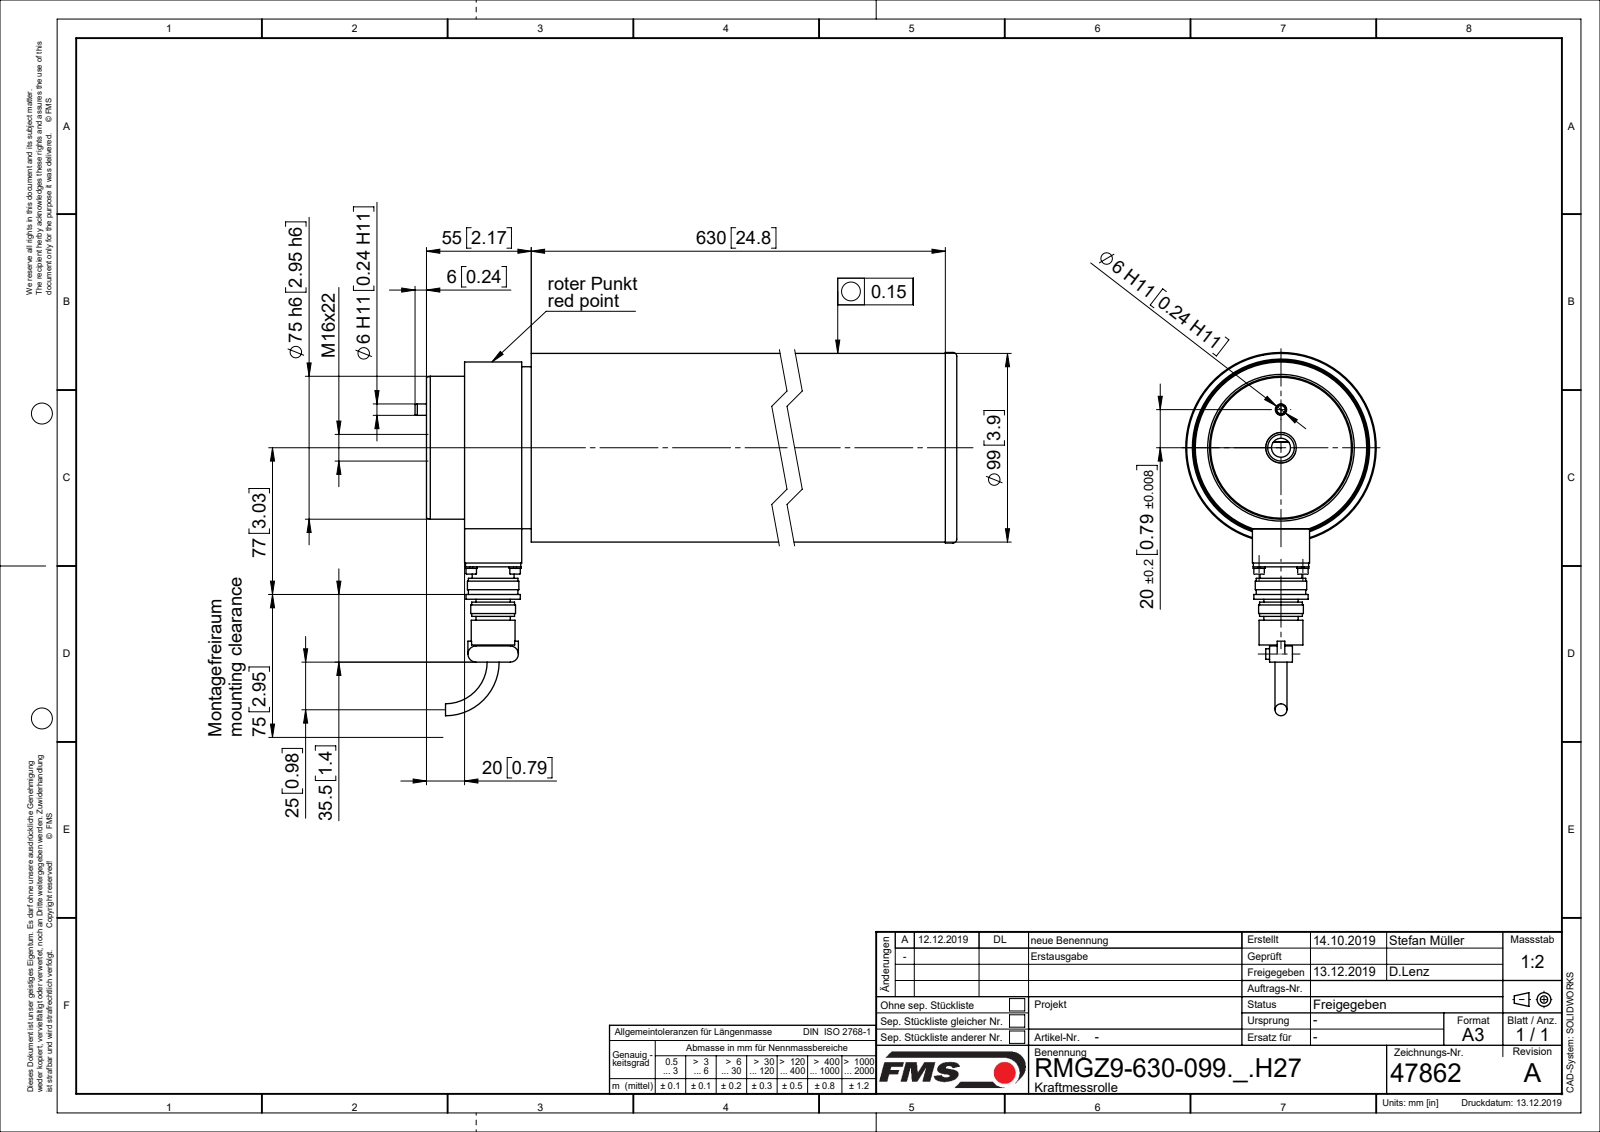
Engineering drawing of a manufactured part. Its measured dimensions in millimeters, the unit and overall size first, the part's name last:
Units: millimetres
Overall size (bounding box): 694 × 190.65 × 100
Round holes (diameter × count): ⌀2.6 ×4, ⌀3.4 ×4, ⌀10 ×1, ⌀12 ×1, ⌀14.21 ×1, ⌀22 ×1, ⌀23 ×1, ⌀26 ×1, ⌀40 ×1, ⌀48.68 ×1, ⌀75 ×1, ⌀81 ×1
Round bosses / shafts (diameter × count): ⌀2.5 ×4, ⌀5.5 ×2, ⌀100 ×1, ⌀99 ×1, ⌀90 ×1, ⌀86 ×1, ⌀85 ×1, ⌀68 ×1
Partial cylindrical surfaces — rounded edges, fillets, slot ends (radius × count): R4.25 ×2, R27.5 ×1
Main face-to-face distances: 20, 50, 158, 5, 297, 284, 442, 35, 139, 227
Hole centre spacings: 16.26, 23, 32.53
Volume: 2 296 000 mm³ · Surface area: 644 177 mm²
Bodies: 11 solids, 352 faces (106 planar, 158 cylindrical, 88 other)
Part name (STEP PRODUCT): R47862; R4767404; TEIL1; R47849 (+8 more)
STEP written by: Mechanical Desktop 2007 (CONFIG_CONTROL_DESIGN)
